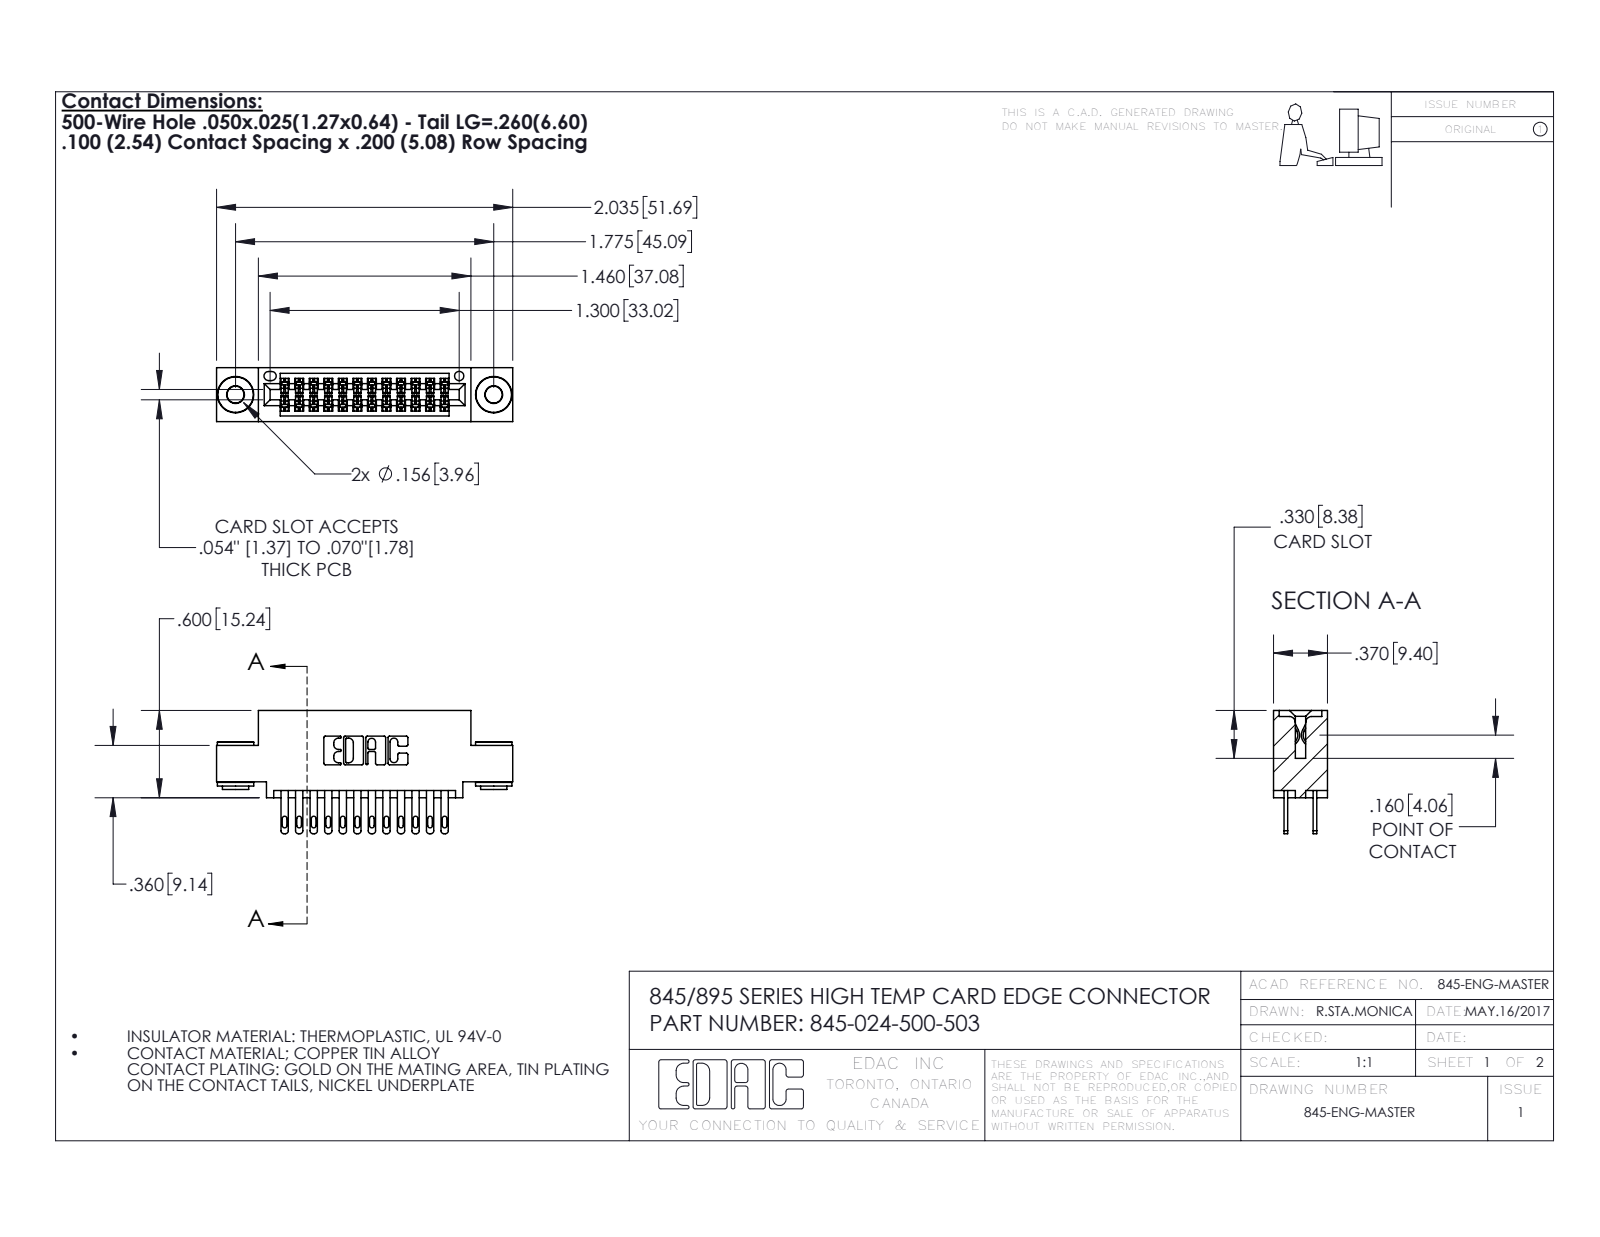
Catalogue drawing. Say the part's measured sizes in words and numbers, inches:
The part is named "345 Part_0.110 Offset - 0.156 Dia-TH; 345-292-001_345-293-100; 345-250-002_345-250-002-102; 345-024-500-503". Its 3-D file was written by "SolidWorks 2016 (CONFIG_CONTROL_DESIGN)". It is 27 solids with 1272 faces: 742 planar, 522 cylindrical and 8 other. Overall it measures 2.035 by 0.847 by 0.37 inches. Its volume is 0.291 cubic inches and its surface area 10.85 square inches. Round holes: 2 of diameter 0.116, 2 of diameter 0.156, 1 of diameter 0.064. Round bosses or shafts: 2 of diameter 0.25, 2 of diameter 0.18, 2 of diameter 0.136. Partial cylindrical surfaces (rounded edges, fillets, slot ends): 36 of radius 0.006, 24 of radius 0.016, 24 of radius 0.02, 22 of radius 0.01, 6 of radius 0.007, 6 of radius 0.031, 3 of radius 0.026, 2 of radius 0.014. The main face-to-face distances are 0.072, 0.298, 0.2, 0.025, 0.098, 0.272, 0.37, 0.225, 0.1, 0.175. The hole center spacings are 0.27, 1.543, 1.775.
